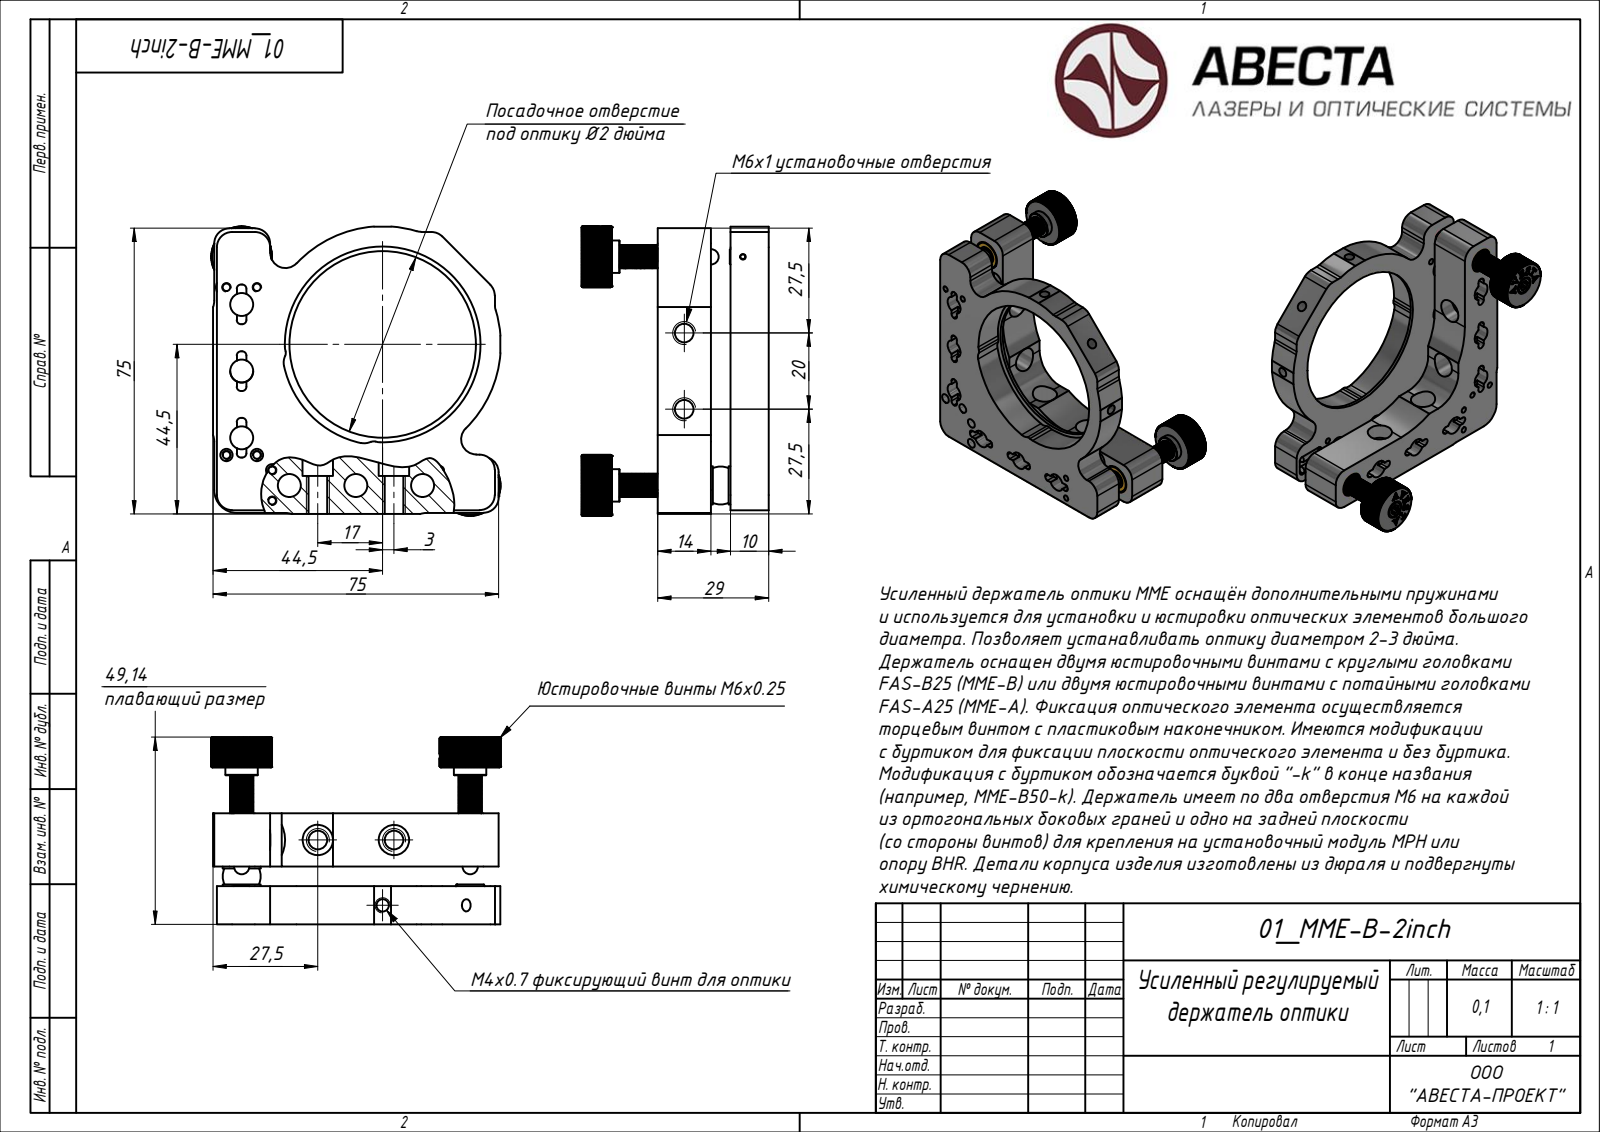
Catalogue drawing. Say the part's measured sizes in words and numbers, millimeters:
Its 3-D file was written by "ST-DEVELOPER v15 (AUTOMOTIVE_DESIGN)". It is 52 solids with 2535 faces: 1109 planar, 0 cylindrical and 1426 other. Overall it measures 212.11 by 122.71 by 98.18 millimeters. Its volume is 226 831 cubic millimeters and its surface area 122 048 square millimeters. The main face-to-face distances are 14, 76.88, 77.48, 0.64, 10, 11, 1, 19.15, 19.14, 0.63.
